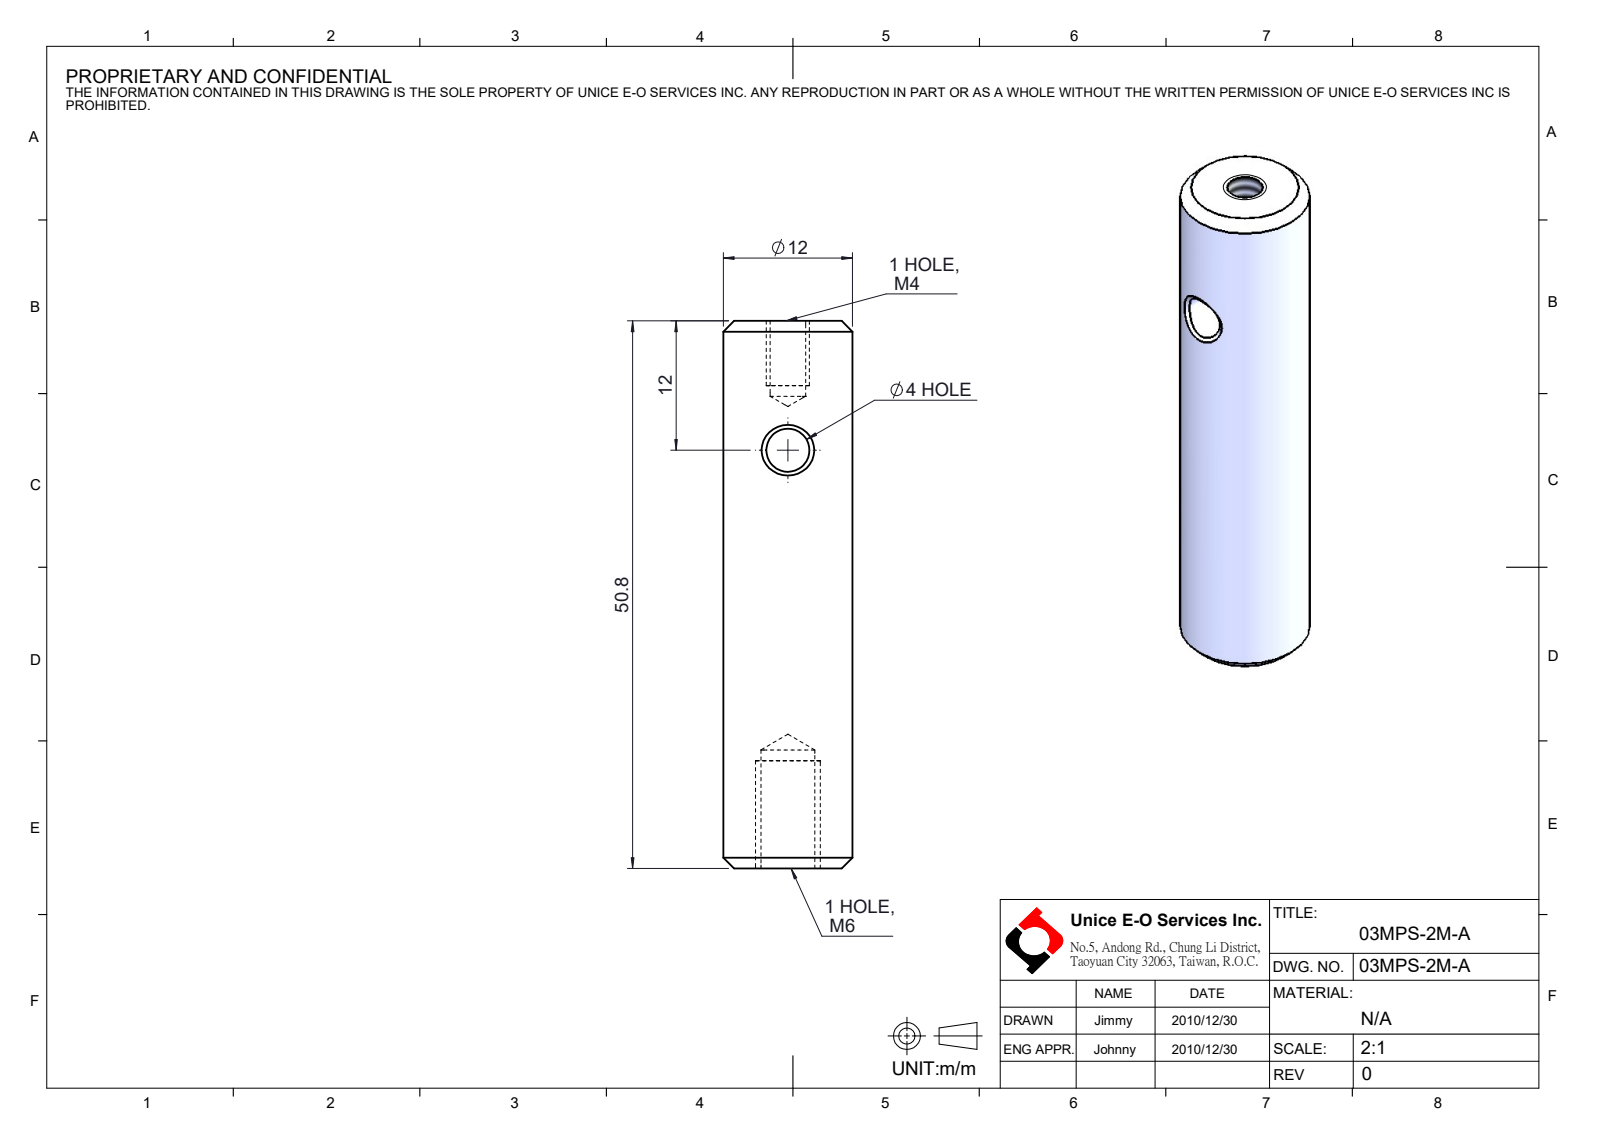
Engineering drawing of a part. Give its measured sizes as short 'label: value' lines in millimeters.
name: 03MPS-2M-A
written by: SolidWorks 2016 (CONFIG_CONTROL_DESIGN)
unit: mm
bodies: 1 solid, 22 faces (2 planar, 8 cylindrical, 12 other)
size: 50.8 × 12 × 12
volume: 5 271 mm³; area: 2 459 mm²
holes: 1× ⌀3.3, 1× ⌀4, 1× ⌀5
bosses: 1× ⌀12
face distances: 50.8
